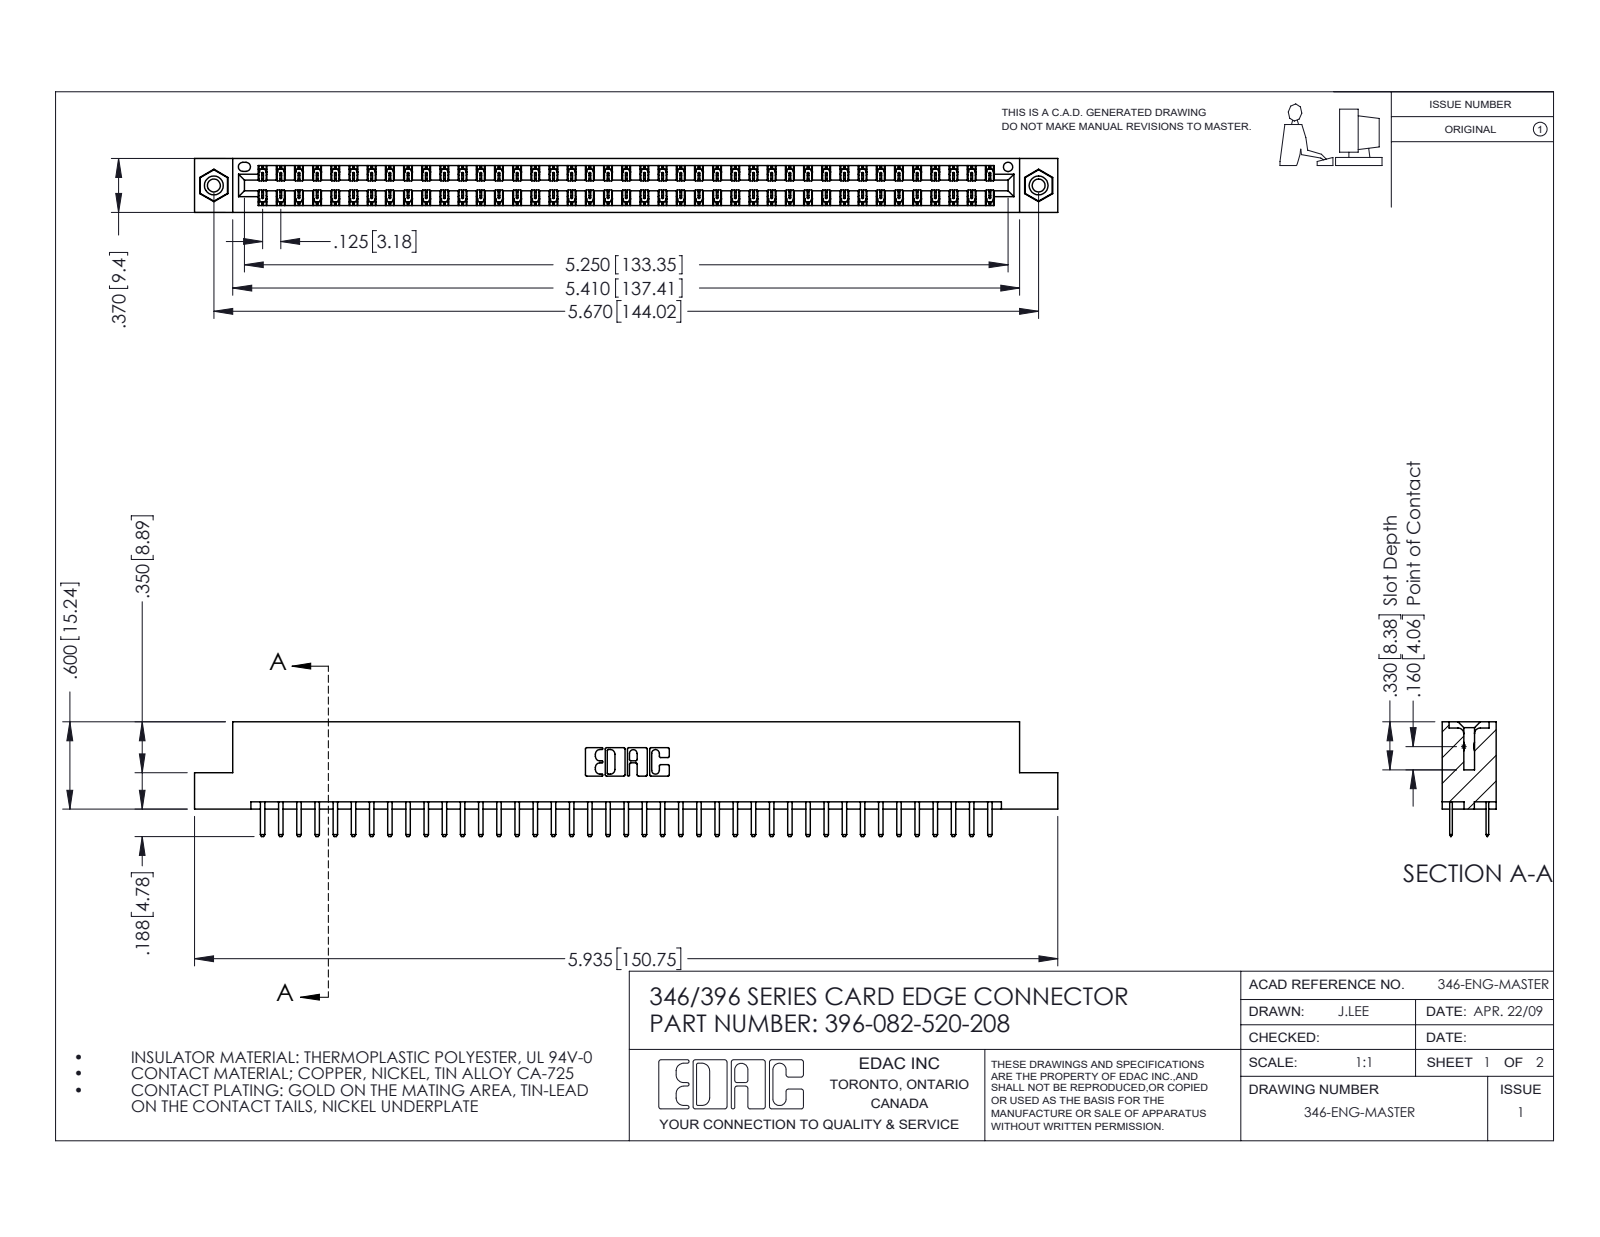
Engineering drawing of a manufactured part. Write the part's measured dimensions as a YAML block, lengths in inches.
part_name: "345-292-001_345-293-120; 396-082-520-208; 346 Part_Flush Mounting Lugs - 0.156 Dia-TI; 345-250-001_345-250-003-102"
step_written_by: "SolidWorks 2016 (CONFIG_CONTROL_DESIGN)"
units: inches
bodies: {solids: 85, faces: 4774, planar: 3142, cylindrical: 1616, other: 16}
overall_size: [5.935, 0.788, 0.37]
volume: 0.894
surface_area: 31.09
round_holes:
  - {diameter: 0.089, count: 2}
  - {diameter: 0.125, count: 2}
  - {diameter: 0.156, count: 2}
  - {diameter: 0.064, count: 1}
round_bosses_or_shafts:
  - {diameter: 0.155, count: 2}
partial_cylinders:
  - {radius: 0.006, count: 123}
  - {radius: 0.01, count: 86}
  - {radius: 0.01, count: 22}
  - {radius: 0.007, count: 6}
  - {radius: 0.031, count: 6}
  - {radius: 0.026, count: 3}
  - {radius: 0.014, count: 2}
  - {radius: 0.022, count: 2}
face_to_face_distances: [0.048, 0.322, 0.25, 0.37, 0.275, 0.072, 0.298, 0.025, 0.148, 0.222]
hole_center_spacings: [0.246, 5.461, 5.67]
